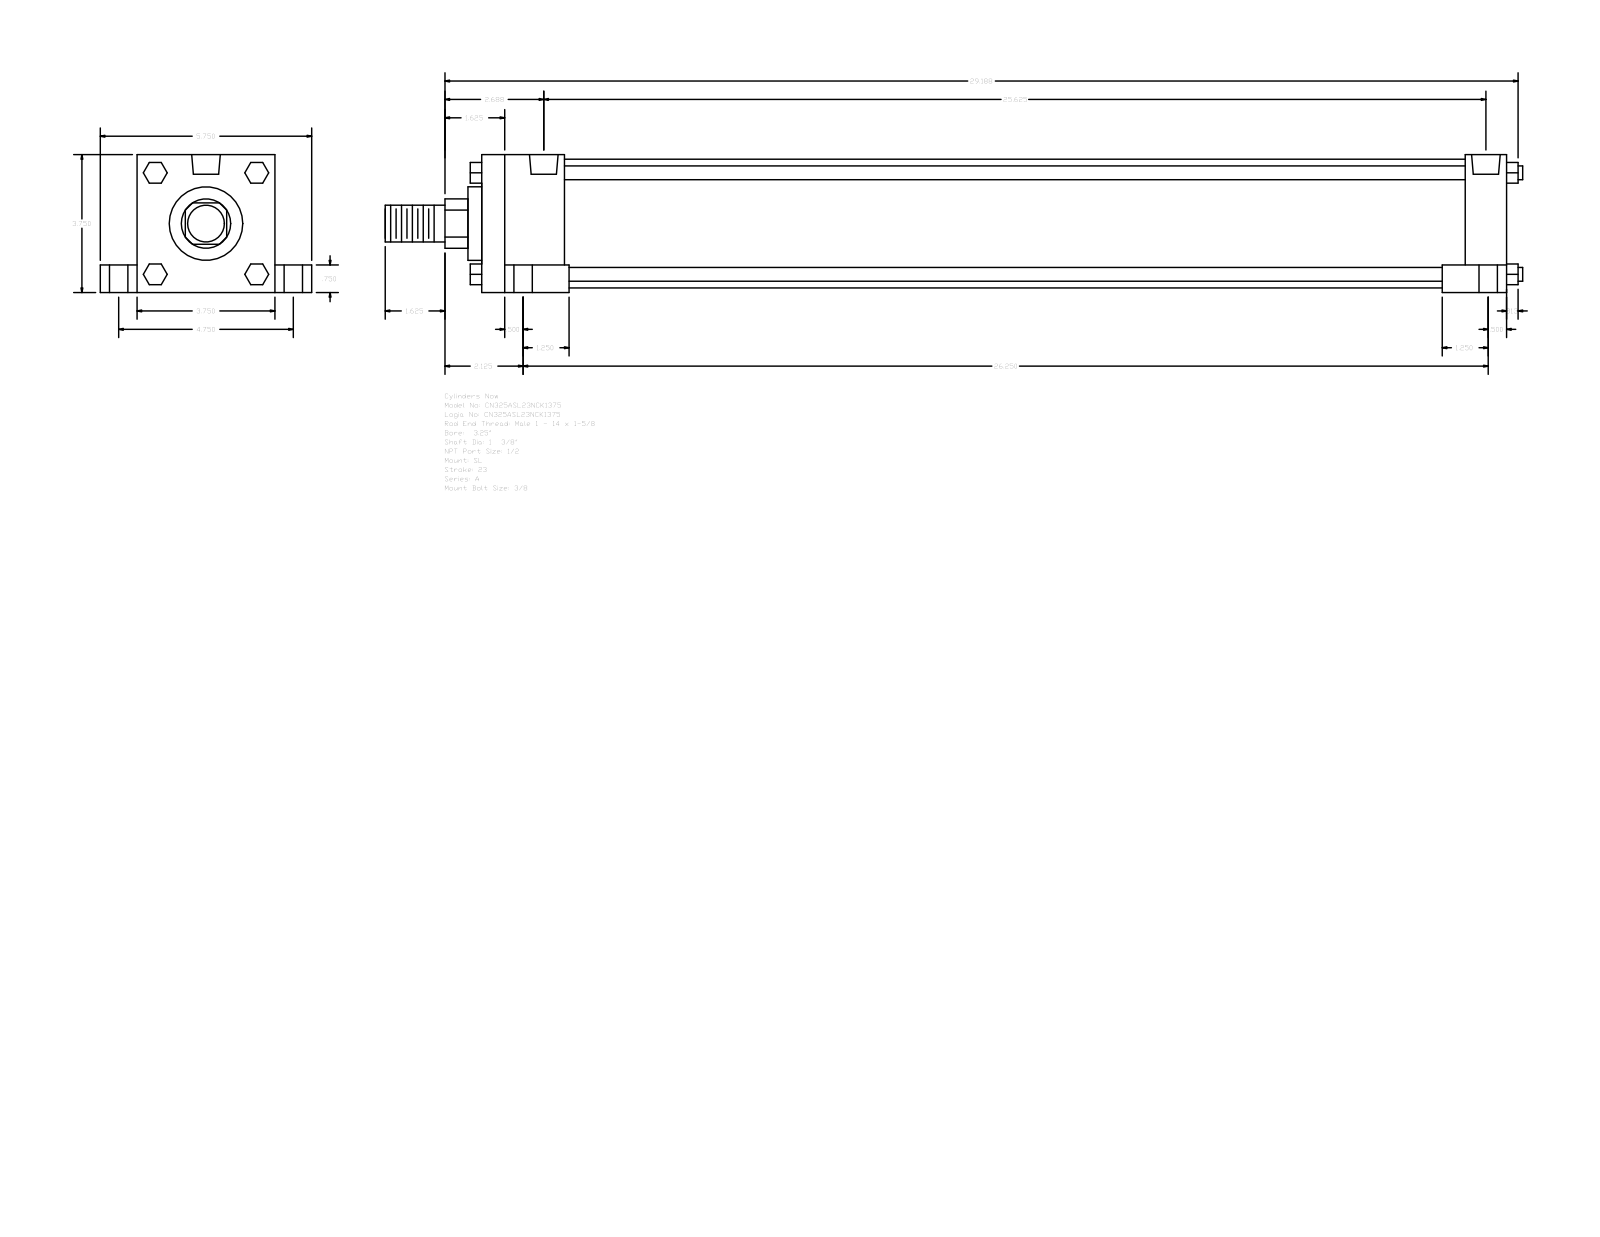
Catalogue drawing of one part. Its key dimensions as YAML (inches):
part_name: "A_SL__0325_1.375"
step_written_by: "GSSL Pune (CONFIG_CONTROL_DESIGN)"
units: inches
bodies: {solids: 0, faces: 150, planar: 114, cylindrical: 36, other: 0}
overall_size: [30.937, 5.75, 3.75]
round_holes:
  - {diameter: 0.344, count: 4}
  - {diameter: 0.5, count: 4}
  - {diameter: 0.75, count: 4}
  - {diameter: 0.778, count: 2}
round_bosses_or_shafts:
  - {diameter: 0.375, count: 4}
  - {diameter: 3.5, count: 1}
  - {diameter: 2, count: 1}
  - {diameter: 1.375, count: 1}
  - {diameter: 1, count: 1}
partial_cylinders:
  - {radius: 0.672, count: 1}
face_to_face_distances: [3.75, 27.875, 1, 4.75, 0.75, 3, 2.25, 1.125, 26.75, 24.5]
hole_center_spacings: [0.125, 2.376, 2.383, 2.441, 2.473, 4.75, 25.375, 25.5]
